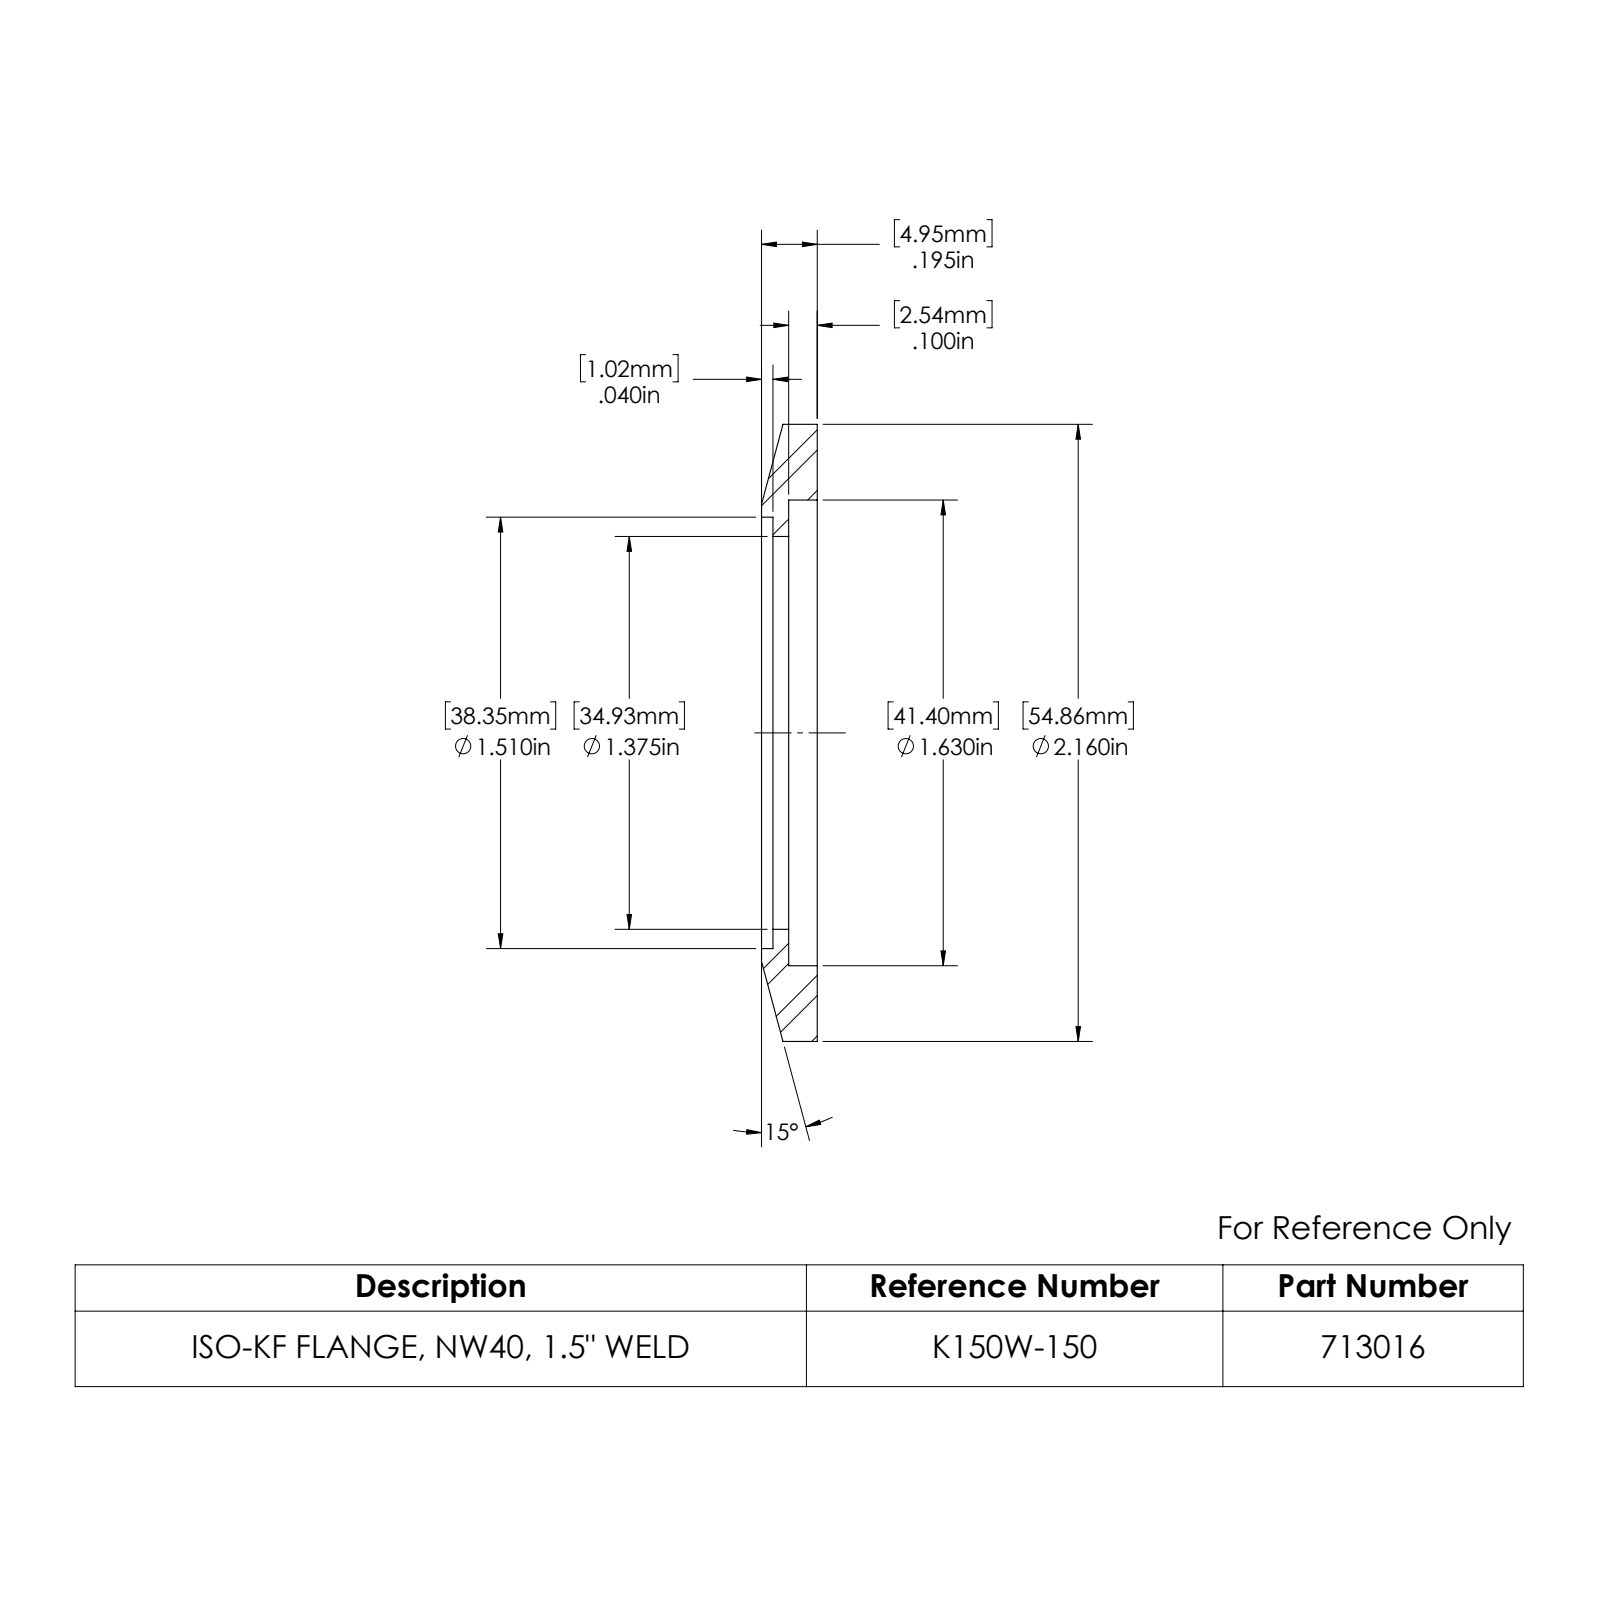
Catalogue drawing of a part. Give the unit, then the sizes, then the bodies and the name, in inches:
Units: inches
Overall size (bounding box): 2.16 × 2.16 × 0.195
Round holes (diameter × count): ⌀1.375 ×1, ⌀1.51 ×1, ⌀1.63 ×1
Round bosses / shafts (diameter × count): ⌀2.16 ×1
Main face-to-face distances: 0.1, 0.155, 0.055, 0.195, 0.095, 0.04
Volume: 0.288 in³ · Surface area: 6.171 in²
Bodies: 1 solid, 14 faces (4 planar, 8 cylindrical, 2 other)
Part name (STEP PRODUCT): 713016
STEP written by: SolidWorks 2022 (AUTOMOTIVE_DESIGN)
